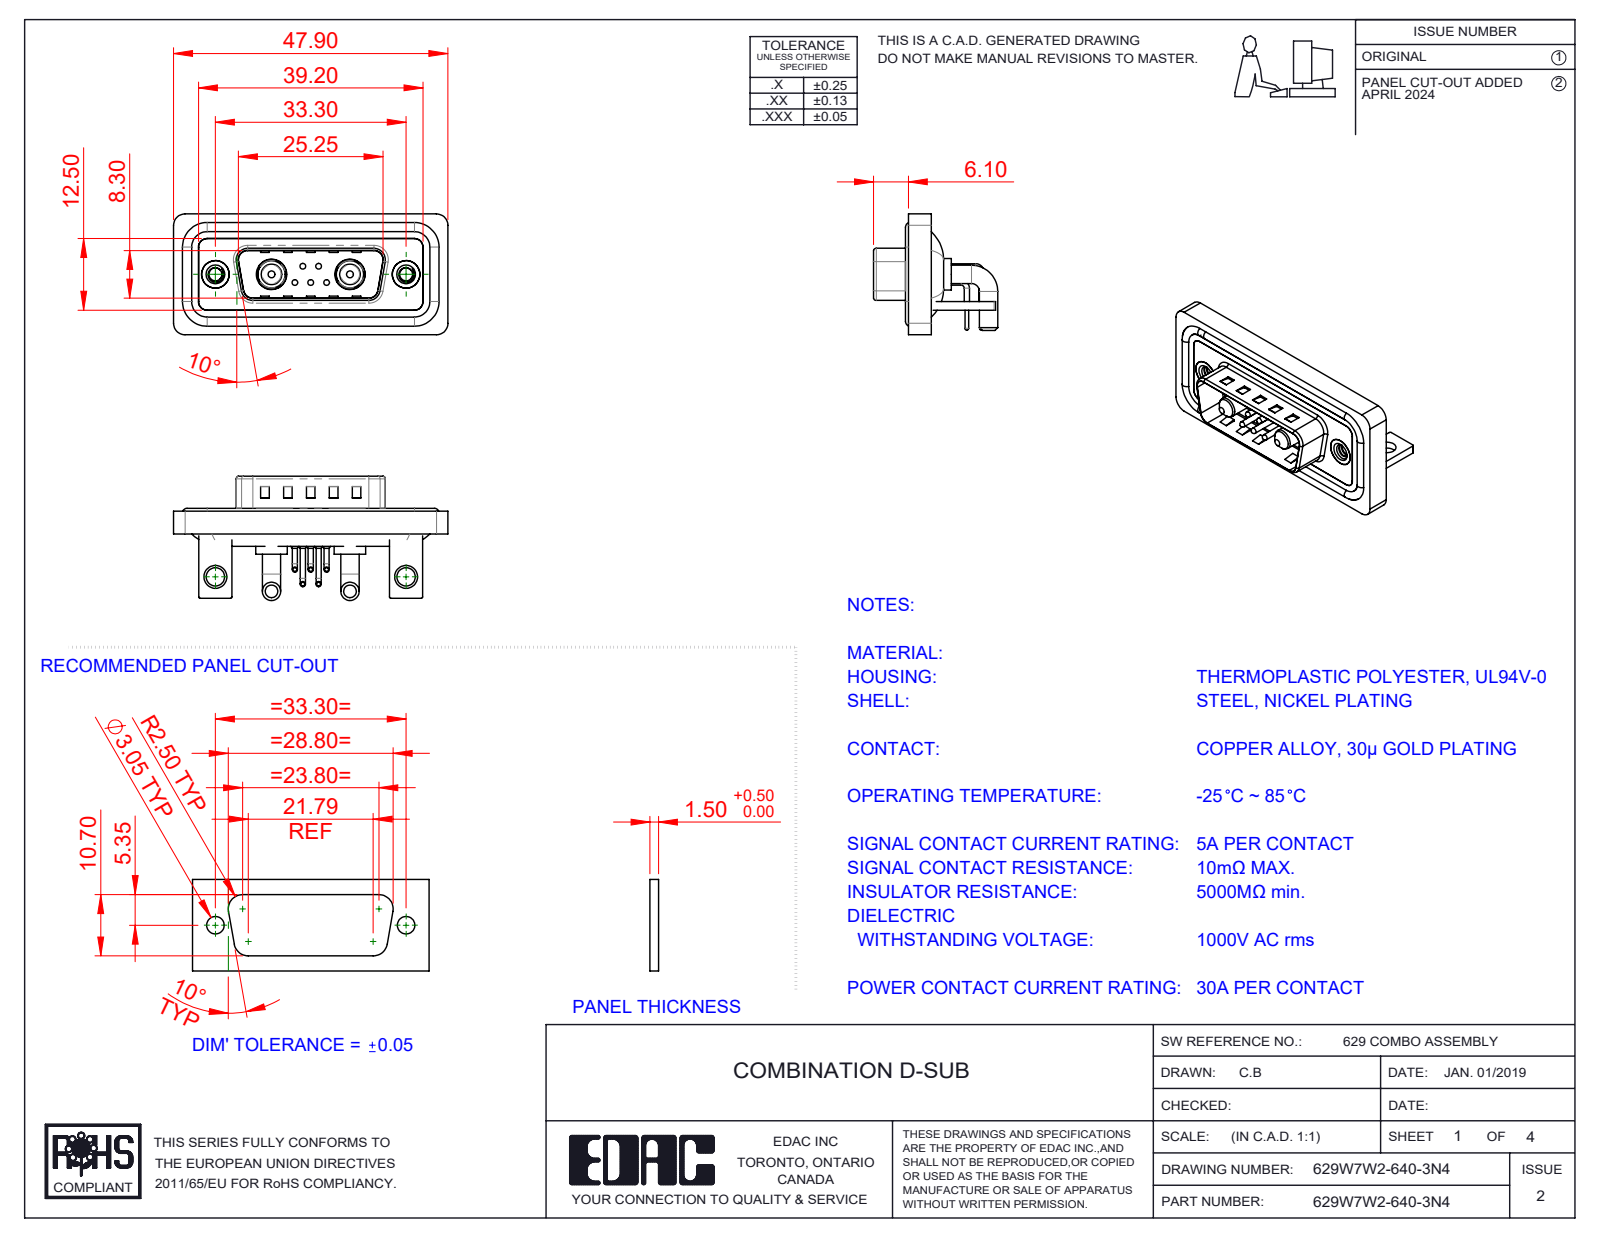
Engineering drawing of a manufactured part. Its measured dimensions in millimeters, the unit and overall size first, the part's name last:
Units: millimetres
Overall size (bounding box): 47.9 × 21.7 × 21.1
Round holes (diameter × count): ⌀0.75 ×5, ⌀1.6 ×5, ⌀2 ×5, ⌀2.26 ×2, ⌀3.2 ×2, ⌀4 ×2, ⌀4.8 ×2, ⌀4.85 ×2, ⌀5 ×2, ⌀5.3 ×2
Round bosses / shafts (diameter × count): ⌀0.9 ×10, ⌀1.5 ×5, ⌀1 ×5, ⌀0.65 ×5, ⌀3.2 ×4, ⌀1.6 ×4, ⌀5.5 ×2, ⌀5.2 ×2
Partial cylindrical surfaces — rounded edges, fillets, slot ends (radius × count): R2 ×21, R1.5 ×18, R0.25 ×16, R0.5 ×9, R1.6 ×8, R1.01 ×5, R0.6 ×4, R0.65 ×4
Main face-to-face distances: 0.4, 1.5, 0.8, 2.9, 2.1, 1.1, 1.6, 1.2, 3.7, 4.5
Hole centre spacings: 3.16, 2.77, 9.8, 23.5, 33.3, 4.31, 4.33, 5.03
Volume: 6 014 mm³ · Surface area: 9 764 mm²
Bodies: 18 solids, 1123 faces (537 planar, 424 cylindrical, 162 other)
Part name (STEP PRODUCT): 629Combo Housing_7W2; 629Combo Shell Front_15 Contacts; 629Combo Stabilizer Bracket; 629Combo Shell Rear_15 Contacts (+6 more)
STEP written by: SolidWorks 2023 (CONFIG_CONTROL_DESIGN)
